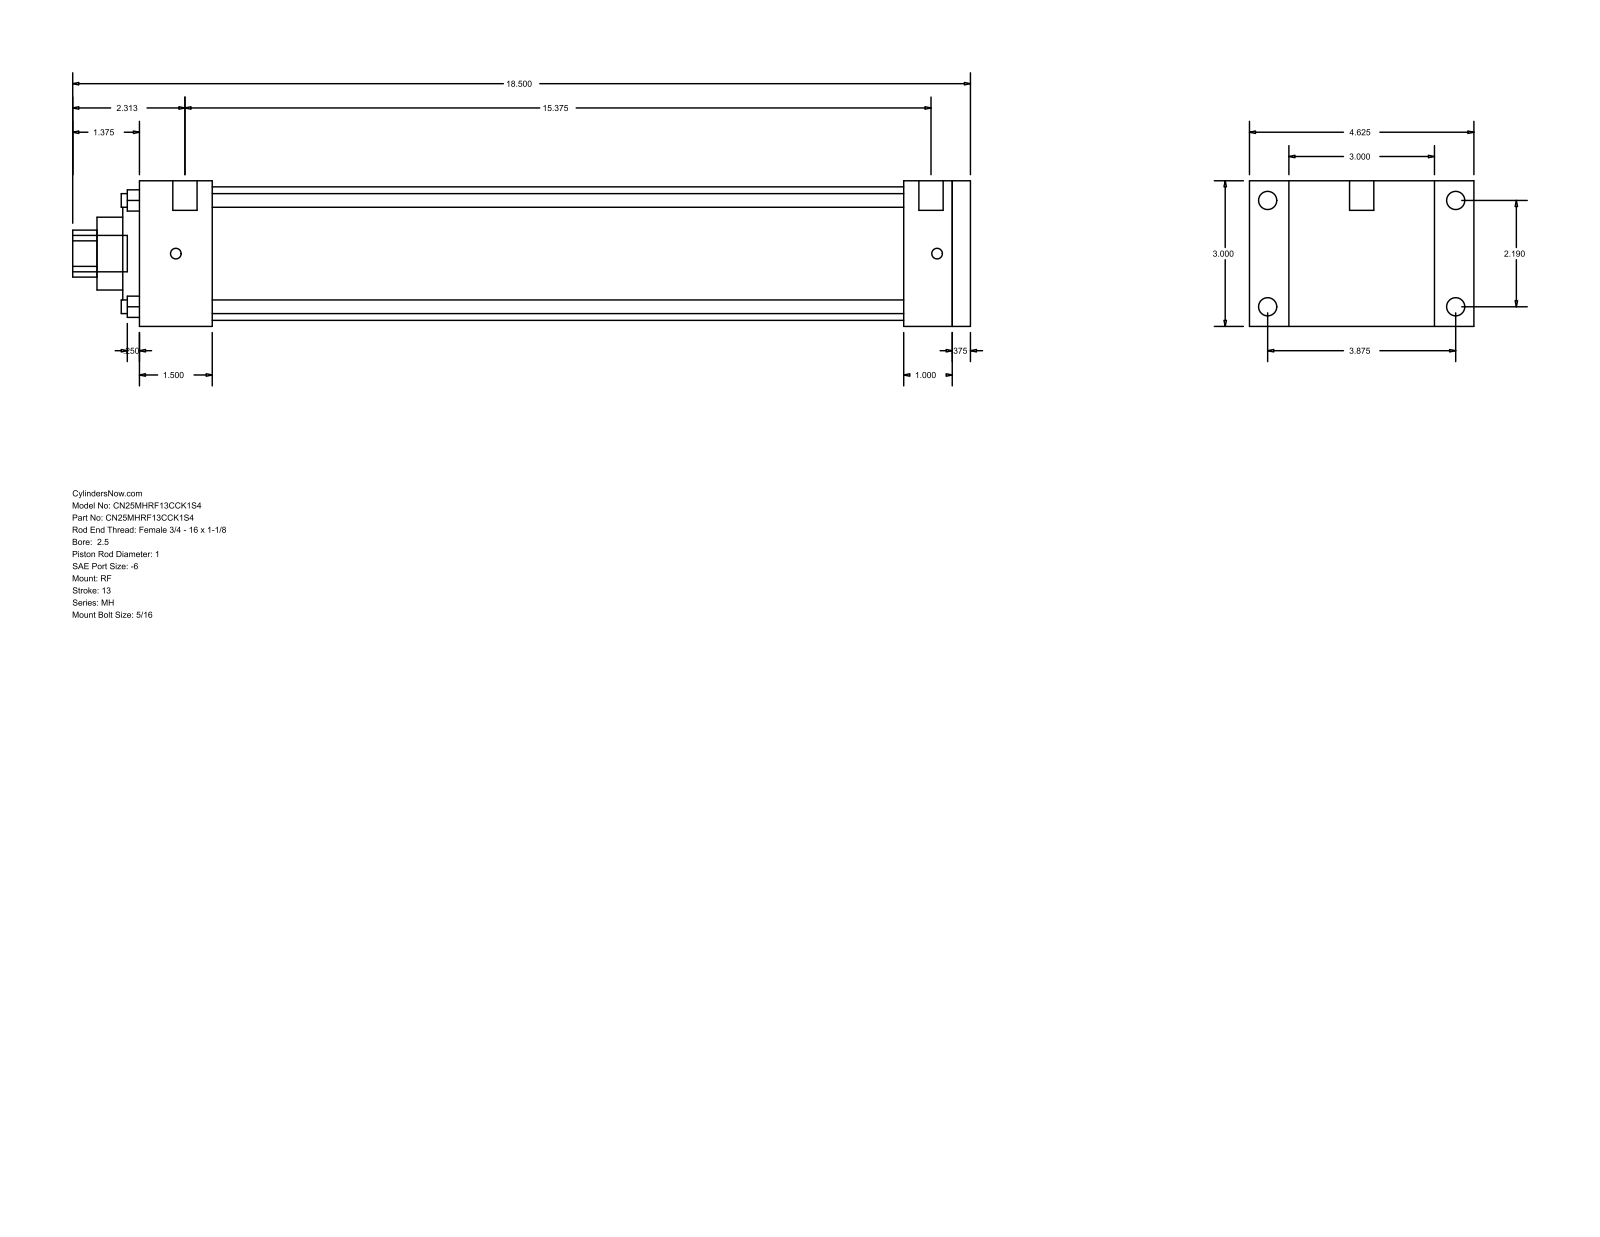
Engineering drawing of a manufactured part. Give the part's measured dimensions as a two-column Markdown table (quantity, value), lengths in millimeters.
| quantity | value |
| --- | --- |
| part name | MH_RF__0250_1 |
| STEP written by | GSSL Pune (CONFIG_CONTROL_DESIGN) |
| units | millimeters |
| bodies | 0 solids, 94 faces (65 planar, 29 cylindrical, 0 other) |
| overall size | 469.9 × 117.47 × 76.2 |
| round holes (diameter × count) | 7.14 × 4, 25.4 × 1, 38.1 × 1, 60.33 × 1, 69.85 × 1 |
| round bosses / shafts (diameter × count) | 9.53 × 4, 5.56 × 4, 12.7 × 2, 19.05 × 1 |
| partial cylindrical surfaces (radius × count) | 12.29 × 1 |
| main face-to-face distances | 76.2, 9.52, 434.98, 425.46, 25.4, 34.92, 400.06, 38.11, 361.95, 387.35 |
| hole center spacings | 39.33, 55.62, 78.66 |
